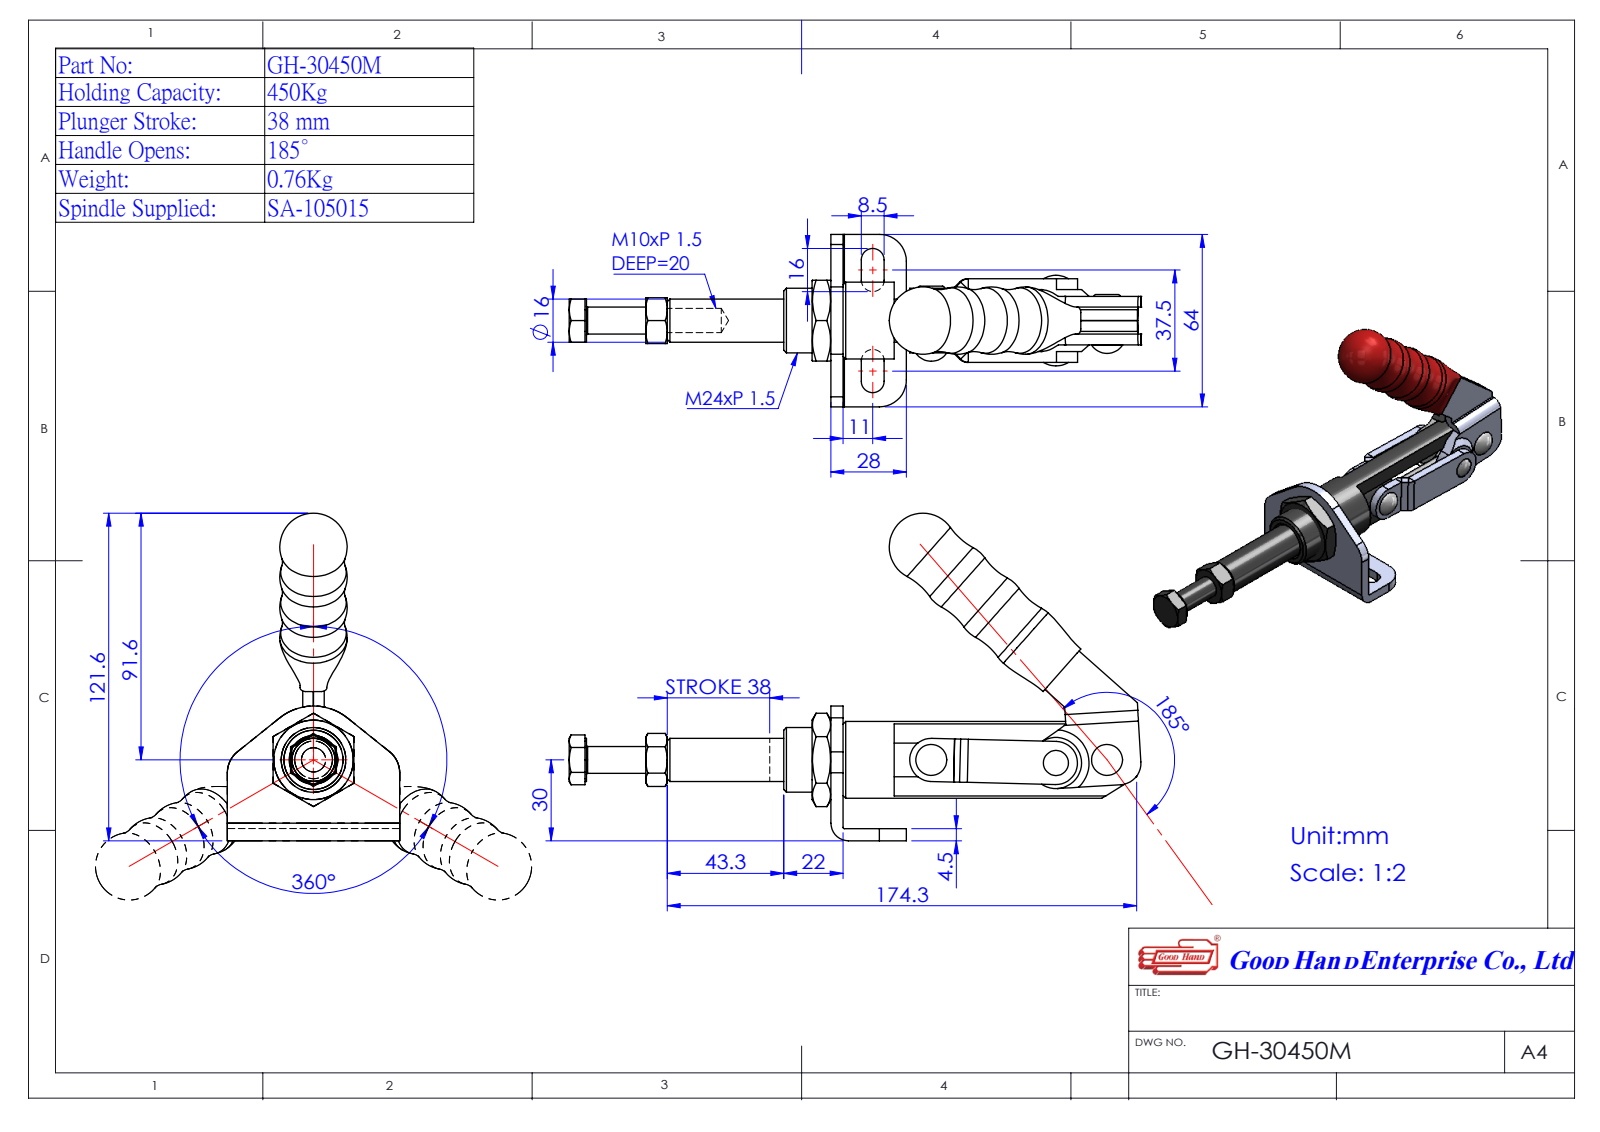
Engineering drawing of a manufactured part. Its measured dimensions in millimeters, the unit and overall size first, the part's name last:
Units: millimetres
Overall size (bounding box): 210.9 × 125.5 × 64
Round holes (diameter × count): ⌀6 ×3, ⌀8.05 ×2, ⌀9 ×1, ⌀22 ×1, ⌀25 ×1
Round bosses / shafts (diameter × count): ⌀28.5 ×1, ⌀24 ×1, ⌀16.02 ×1, ⌀16 ×1, ⌀10 ×1, ⌀9 ×1, ⌀8 ×1, ⌀6 ×1
Partial cylindrical surfaces — rounded edges, fillets, slot ends (radius × count): R3 ×10, R4 ×4, R4.01 ×4, R4.25 ×4, R8 ×3, R0.5 ×1, R6.5 ×1, R9.5 ×1
Main face-to-face distances: 4, 5, 9, 8, 1, 11.5, 4.5, 15.5, 16.5, 20.5
Hole centre spacings: 19, 45, 64
Volume: 121 151 mm³ · Surface area: 64 632 mm²
Bodies: 9 solids, 363 faces (147 planar, 127 cylindrical, 89 other)
Part name (STEP PRODUCT): Group1^GH-30450M(簡化); 13045013(ch-solid-after)-1^GH-30450M(簡化); Group4^GH-30450M(簡化); Group2^GH-30450M(簡化) (+3 more)
STEP written by: SolidWorks 2016 (AUTOMOTIVE_DESIGN)
